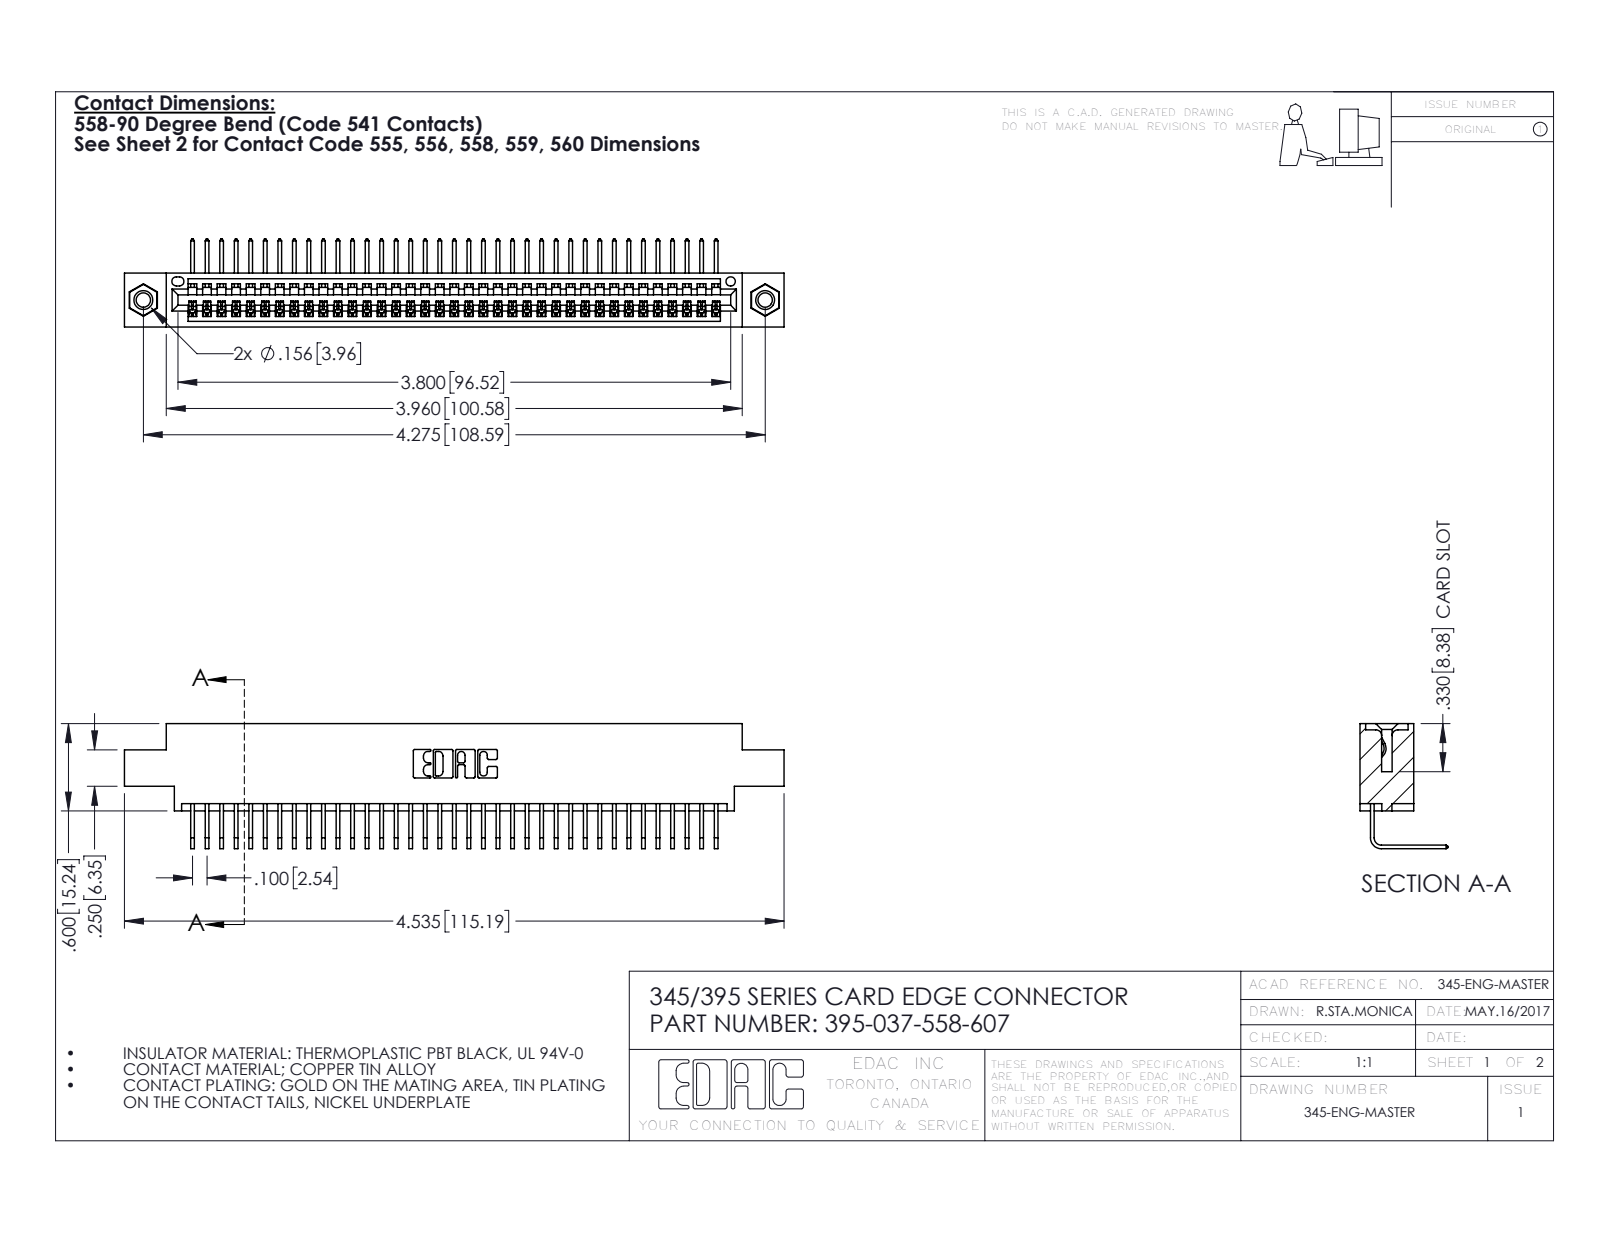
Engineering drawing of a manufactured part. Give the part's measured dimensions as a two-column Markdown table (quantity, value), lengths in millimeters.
| quantity | value |
| --- | --- |
| part name | 345-292-001_558 Tail - 2; 345-250-001_345-250-005-103; 345 Part_0.170 Offset - 0.156 Dia-TI; 395-037-558-607 |
| STEP written by | SolidWorks 2016 (CONFIG_CONTROL_DESIGN) |
| units | millimeters |
| bodies | 40 solids, 2410 faces (1670 planar, 724 cylindrical, 16 other) |
| overall size | 115.2 × 21.8 × 15.4 |
| volume | 10 900 mm³ |
| surface area | 15 300 mm² |
| round holes (diameter × count) | 2.5 × 2, 3.2 × 2, 4 × 2, 1.6 × 1 |
| round bosses / shafts (diameter × count) | 3.9 × 2 |
| partial cylindrical surfaces (radius × count) | 0.2 × 74, 0.3 × 22, 0.2 × 6, 0.8 × 6, 0.7 × 3, 0.8 × 2, 1 × 2, 0.4 × 1 |
| main face-to-face distances | 1.8, 7.6, 9.4, 5.1, 2.5, 6.9, 0.6, 5.7, 4.4, 3.8 |
| hole center spacings | 6.9, 102.6, 108.6 |
